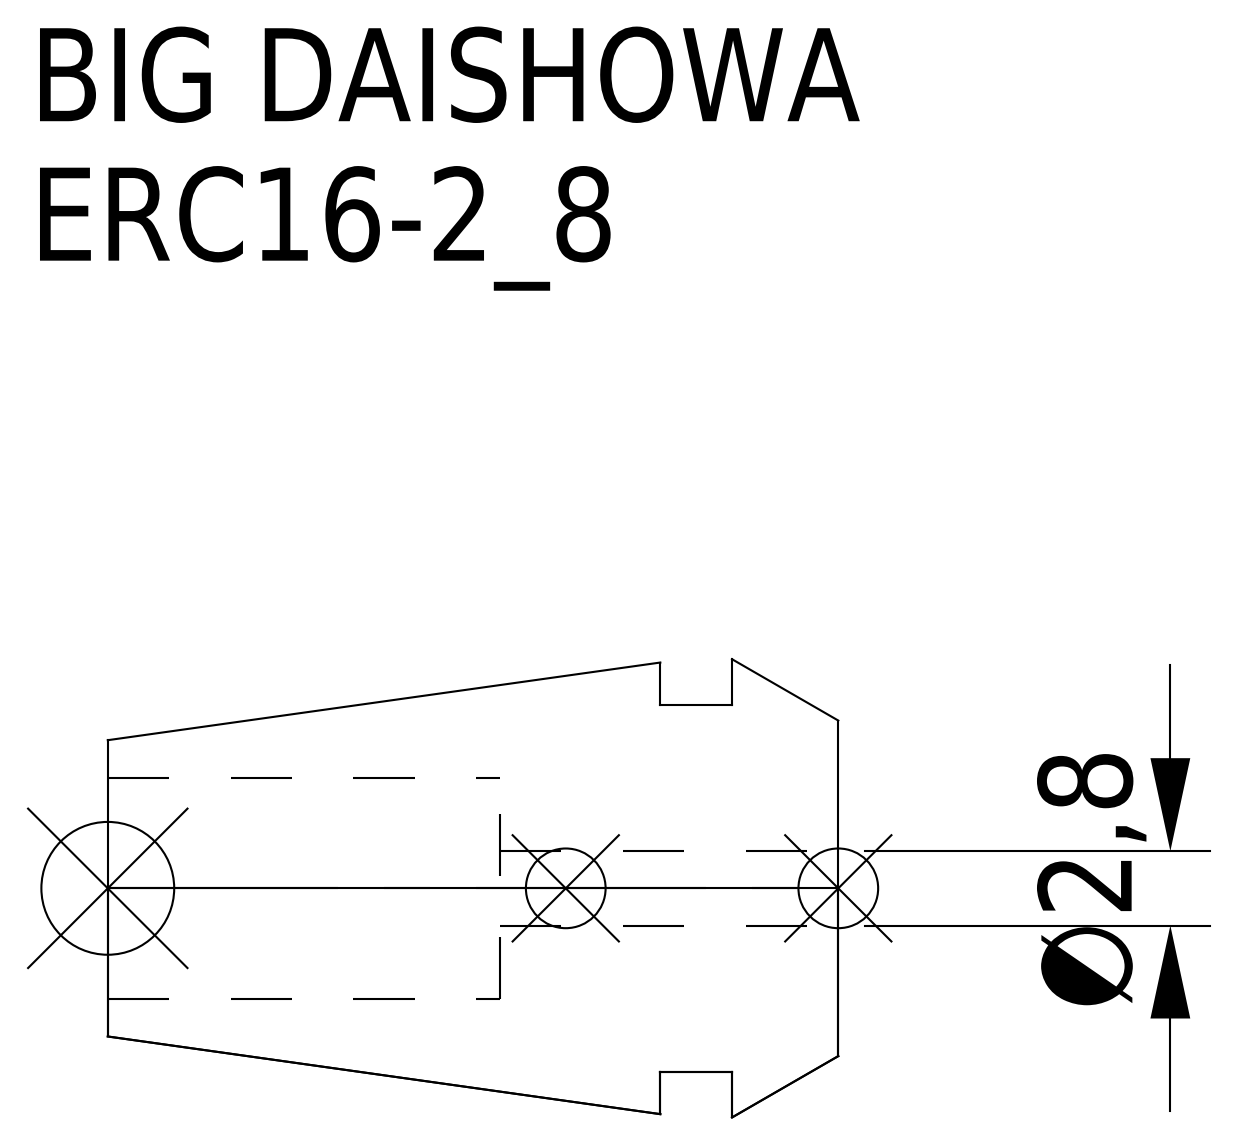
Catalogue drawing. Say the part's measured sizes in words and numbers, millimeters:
The part is named "ERC16-2_8". Its 3-D file was written by "CREO PARAMETRIC BY PTC INC, 2016380 (AUTOMOTIVE_DESIGN)". It is 1 solid with 15 faces: 5 planar, 6 cylindrical and 4 other. Overall it measures 27.5 by 17.25 by 17.25 millimeters. Its volume is 3 517 cubic millimeters and its surface area 2 132 square millimeters. Round holes: 1 of diameter 2.8, 1 of diameter 8.3. Round bosses or shafts: 1 of diameter 13.8. The main face-to-face distances are 4, 6.7, 2.7, 12.73, 8.73, 6.03, 27.5, 23.5, 20.8, 14.77.
